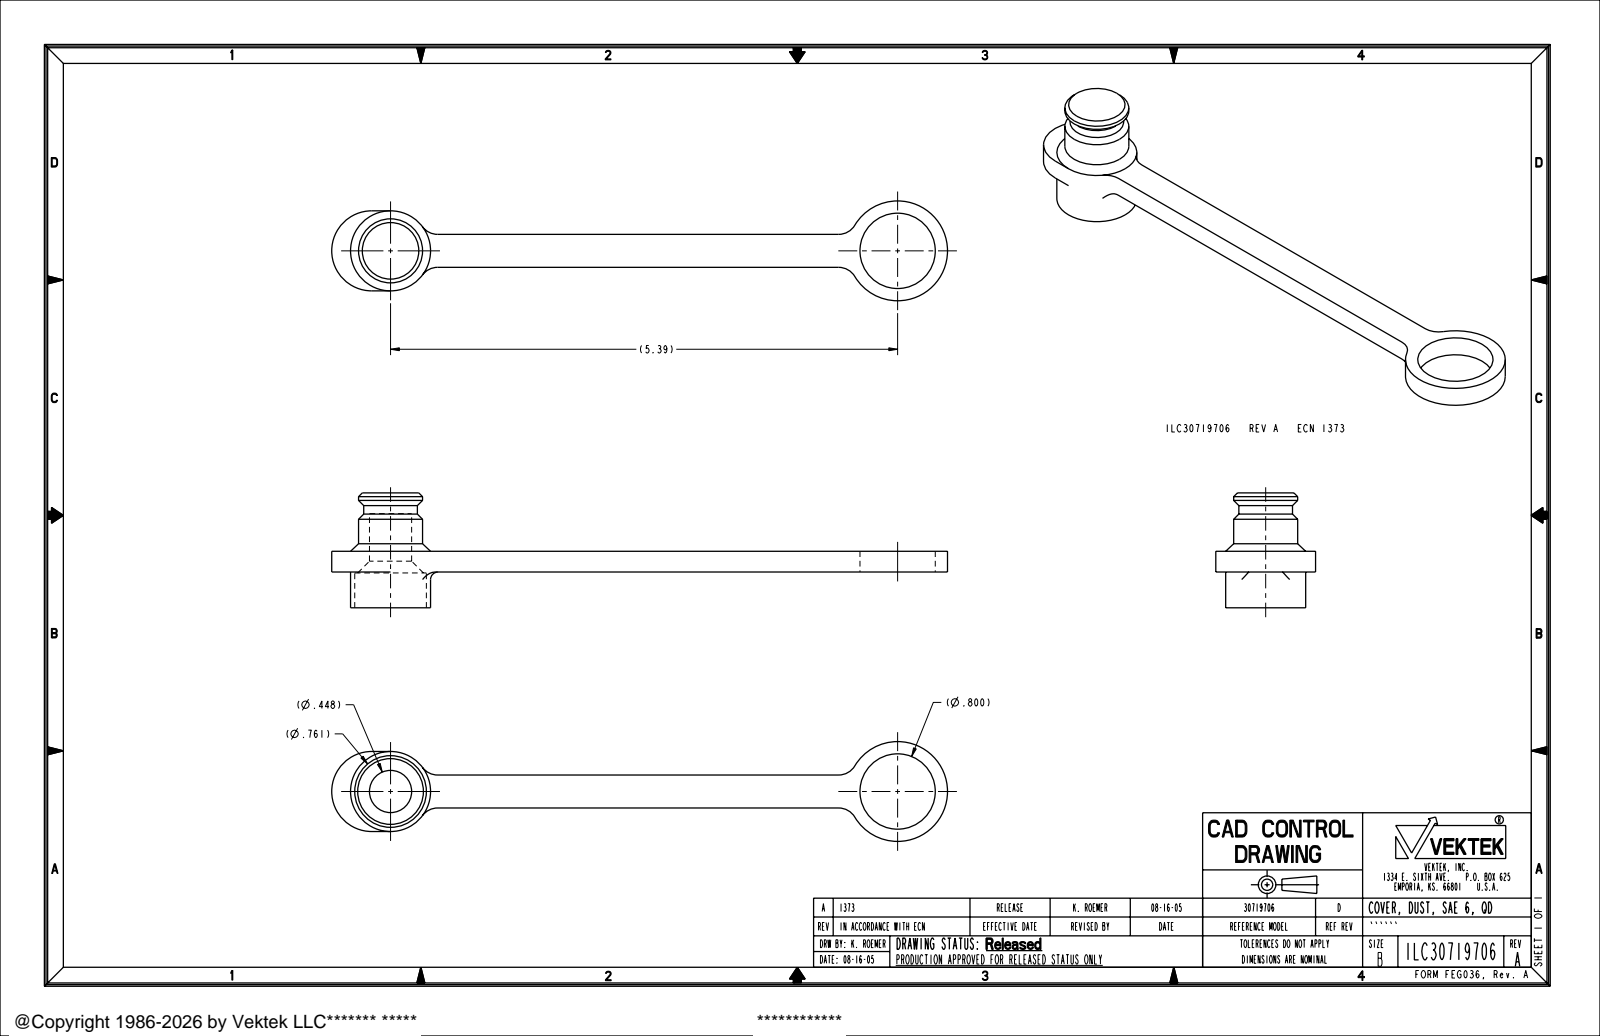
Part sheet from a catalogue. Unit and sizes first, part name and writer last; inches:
Units: inches
Overall size (bounding box): 6.543 × 1.22 × 1.06
Round holes (diameter × count): ⌀0.448 ×1, ⌀0.761 ×1, ⌀0.8 ×1
Round bosses / shafts (diameter × count): ⌀1.06 ×1, ⌀0.85 ×1, ⌀0.68 ×1, ⌀0.57 ×1
Partial cylindrical surfaces — rounded edges, fillets, slot ends (radius × count): R0.2 ×4, R0.425 ×1
Main face-to-face distances: 0.22, 0.35, 0.62, 0.84, 0.4, 0.38, 0.6, 1, 1.22, 0.25
Hole centre spacings: 5.387
Volume: 0.742 in³ · Surface area: 13.04 in²
Bodies: 1 solid, 43 faces (12 planar, 20 cylindrical, 11 other)
Part name (STEP PRODUCT): ILC30719706
STEP written by: PRO/ENGINEER BY PARAMETRIC TECHNOLOGY CORPORATION, 2004290 (AUTOMOTIVE_DESIGN_CC2)
